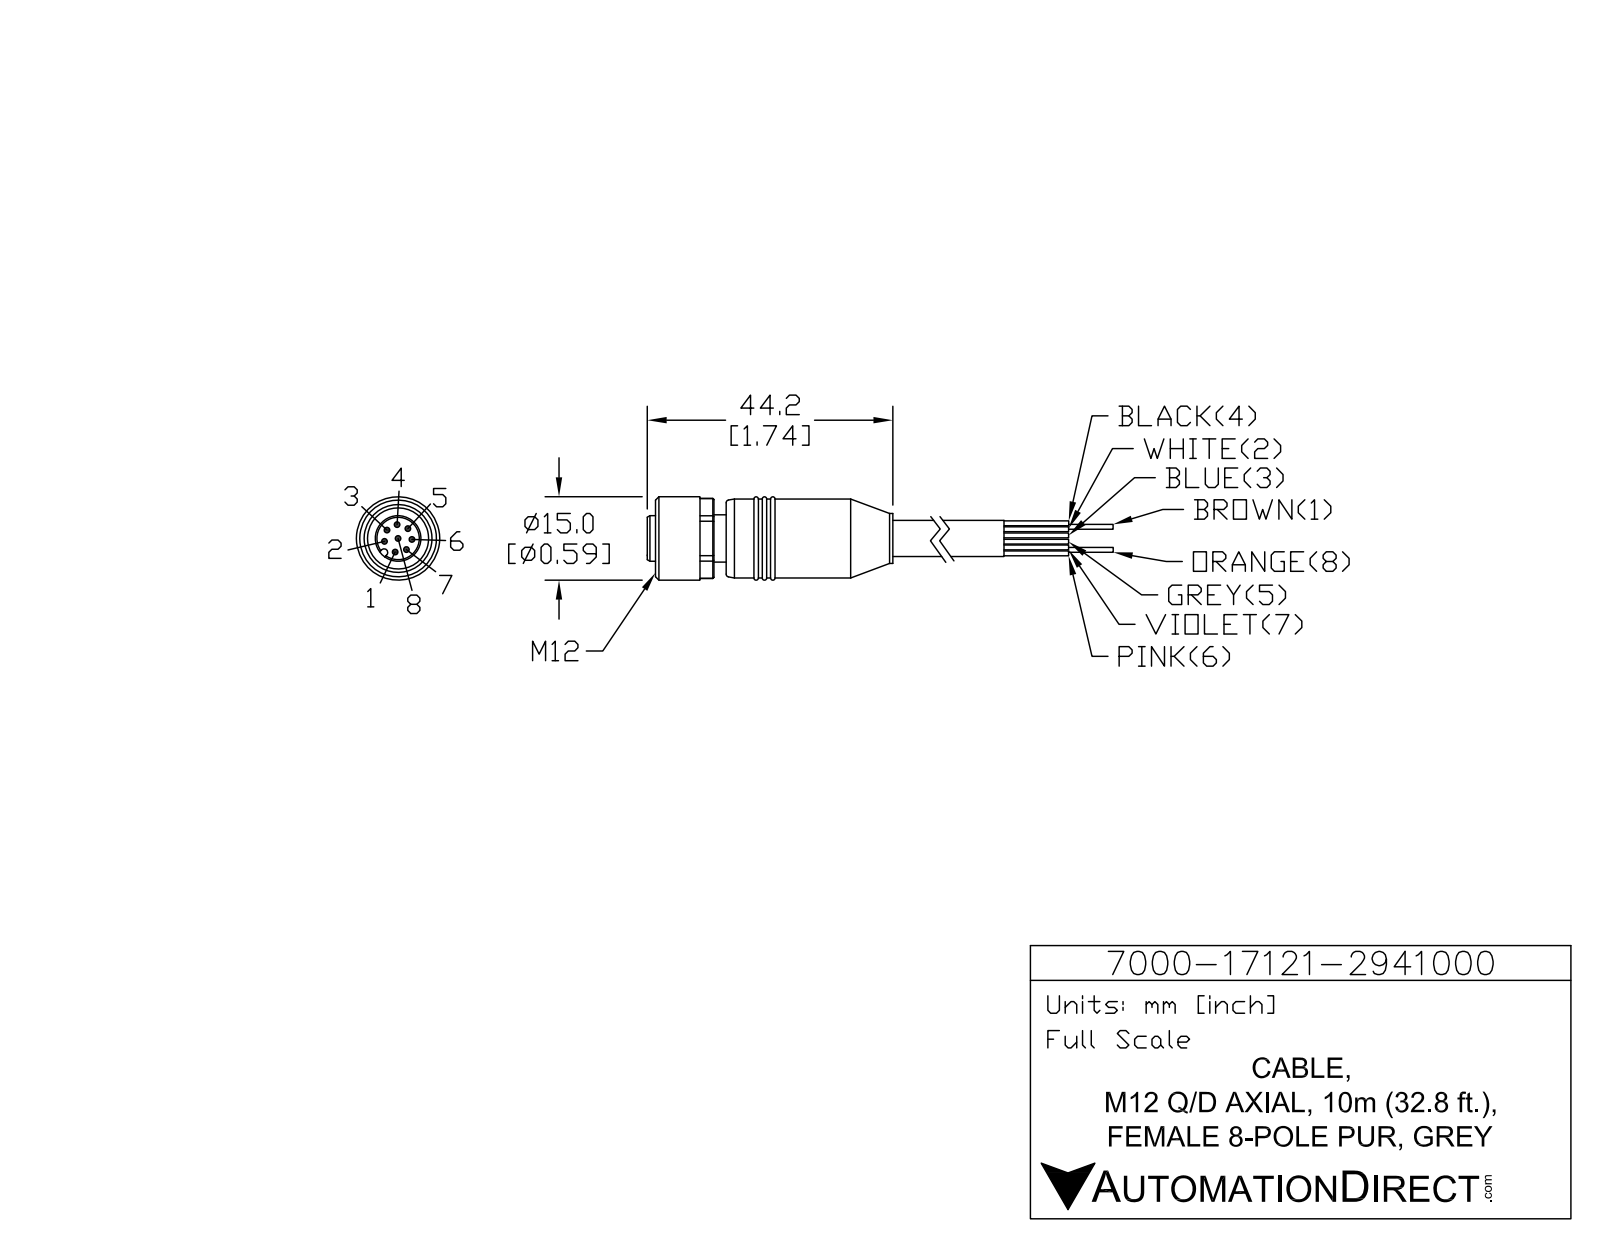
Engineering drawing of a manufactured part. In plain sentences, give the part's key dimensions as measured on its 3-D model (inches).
The part is named "7000-17121-2941000". Its 3-D file was written by "SolidWorks 2015 (AUTOMOTIVE_DESIGN)". It is 1 solid with 103 faces: 31 planar, 44 cylindrical and 28 other. Overall it measures 2.528 by 0.591 by 0.591 inches. Its volume is 0.404 cubic inches and its surface area 5.259 square inches. Round holes: 8 of diameter 0.039, 1 of diameter 0.433. Round bosses or shafts: 1 of diameter 0.591, 1 of diameter 0.559, 1 of diameter 0.354, 1 of diameter 0.335, 1 of diameter 0.323, 1 of diameter 0.256. Partial cylindrical surfaces (rounded edges, fillets, slot ends): 1 of radius 0.026, 1 of radius 0.283. The main face-to-face distances are 0.087, 0.512, 0.118, 0.205, 0.354, 0.472, 0.559, 2.528, 2.173, 2.055. The hole center spacings are 0.098, 0.081, 0.149, 0.195, 0.082, 0.166, 0.189, 0.189.
